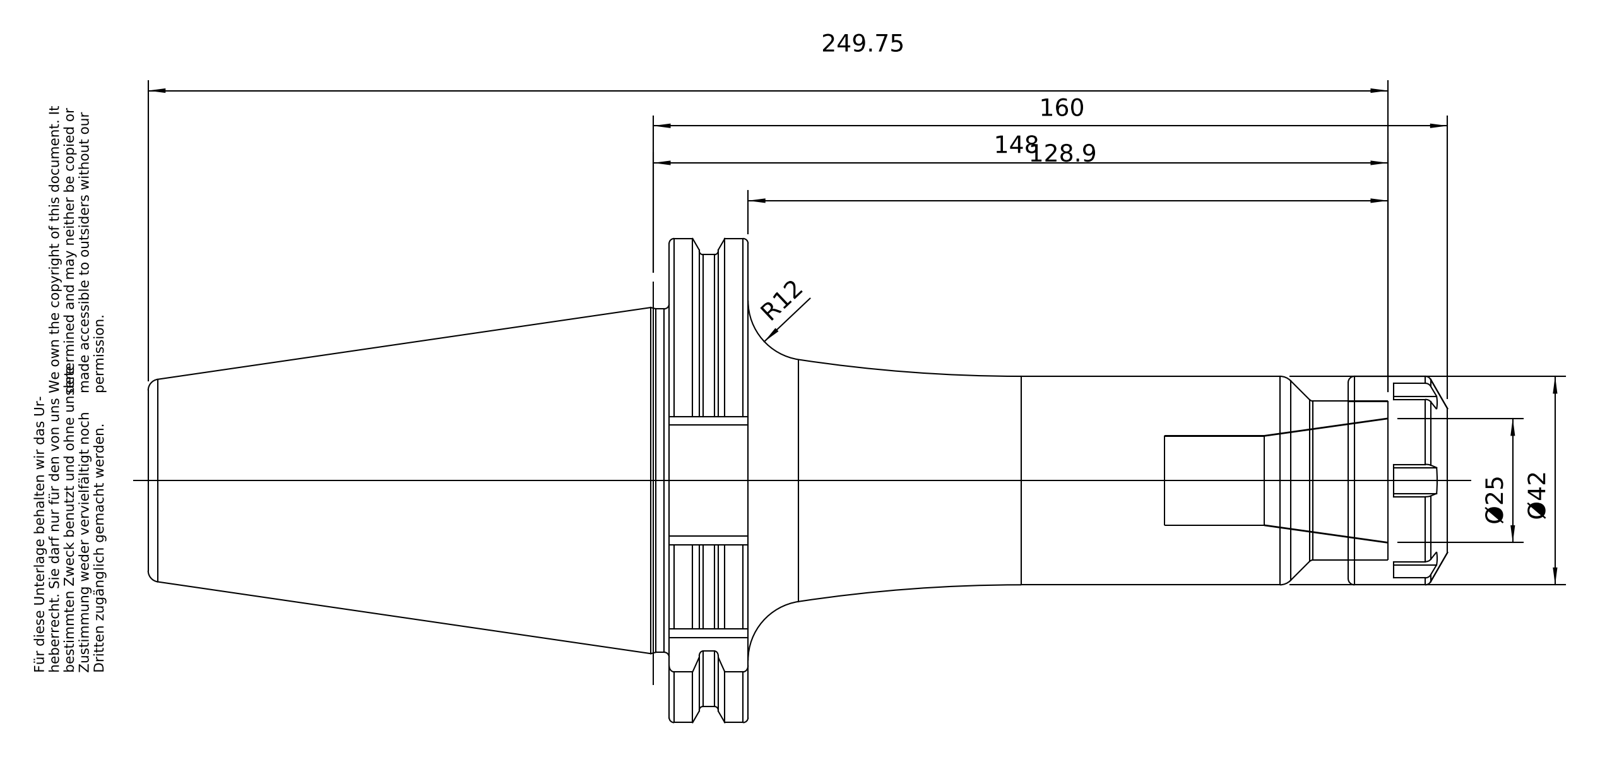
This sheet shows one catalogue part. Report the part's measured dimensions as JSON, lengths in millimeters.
{"part_name": "50-322-25; 83-912-25; 50-322-25_ASM", "step_written_by": "PRO/ENGINEER BY PARAMETRIC TECHNOLOGY CORPORATION, 2010430 (CONFIG_CONTROL_DESIGN)", "units": "millimeters", "bodies": {"solids": 2, "faces": 149, "planar": 41, "cylindrical": 32, "other": 76}, "overall_size": [261.6, 97.47, 94], "volume_mm3": 535733, "surface_area_mm2": 65804, "round_holes": [[18, 1], [20.75, 1], [25.01, 1], [25.7, 1]], "round_bosses_or_shafts": [[91, 1], [69.15, 1], [42, 1], [32, 1], [24.01, 1]], "partial_cylinders_radius": [[1.75, 5], [48.74, 1]], "face_to_face_distances": [15.85, 136.8, 120.95, 156.8, 140.95, 20, 104.8, 120.65, 241.6, 261.6]}
